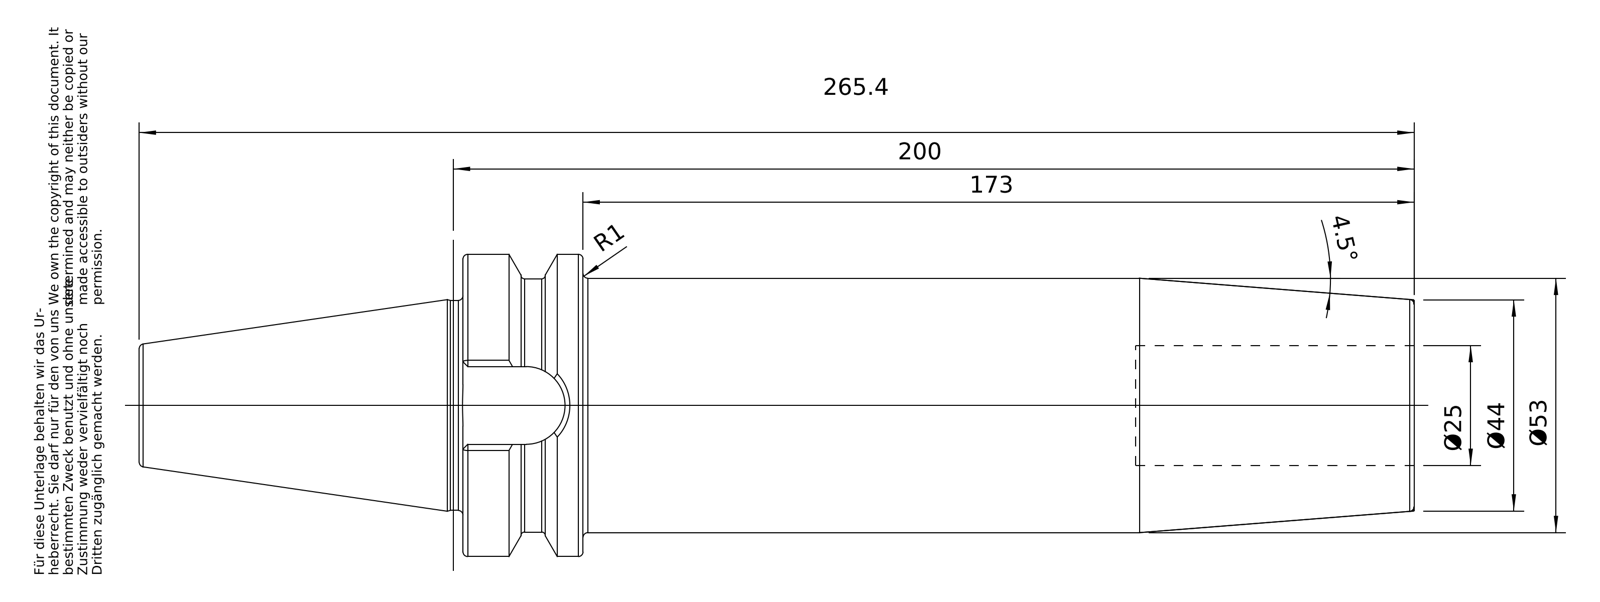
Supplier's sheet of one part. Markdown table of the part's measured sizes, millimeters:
| quantity | value |
| --- | --- |
| part name | 40-646-25 |
| STEP written by | PRO/ENGINEER BY PARAMETRIC TECHNOLOGY CORPORATION, 2010430 (CONFIG_CONTROL_DESIGN) |
| units | millimeters |
| bodies | 1 solid, 96 faces (26 planar, 22 cylindrical, 48 other) |
| overall size | 265.4 × 62.98 × 62.98 |
| volume | 459 144 mm³ |
| surface area | 53 606 mm² |
| round holes (diameter × count) | 13.84 × 1, 17.01 × 1, 17.5 × 1, 25 × 1 |
| round bosses / shafts (diameter × count) | 62.98 × 1, 53 × 1, 52.75 × 1, 43.75 × 1, 16.01 × 1 |
| partial cylindrical surfaces (radius × count) | 8.1 × 1 |
| main face-to-face distances | 198, 25, 173, 140, 115, 58, 44.9, 16.2, 67.4, 92.4 |
